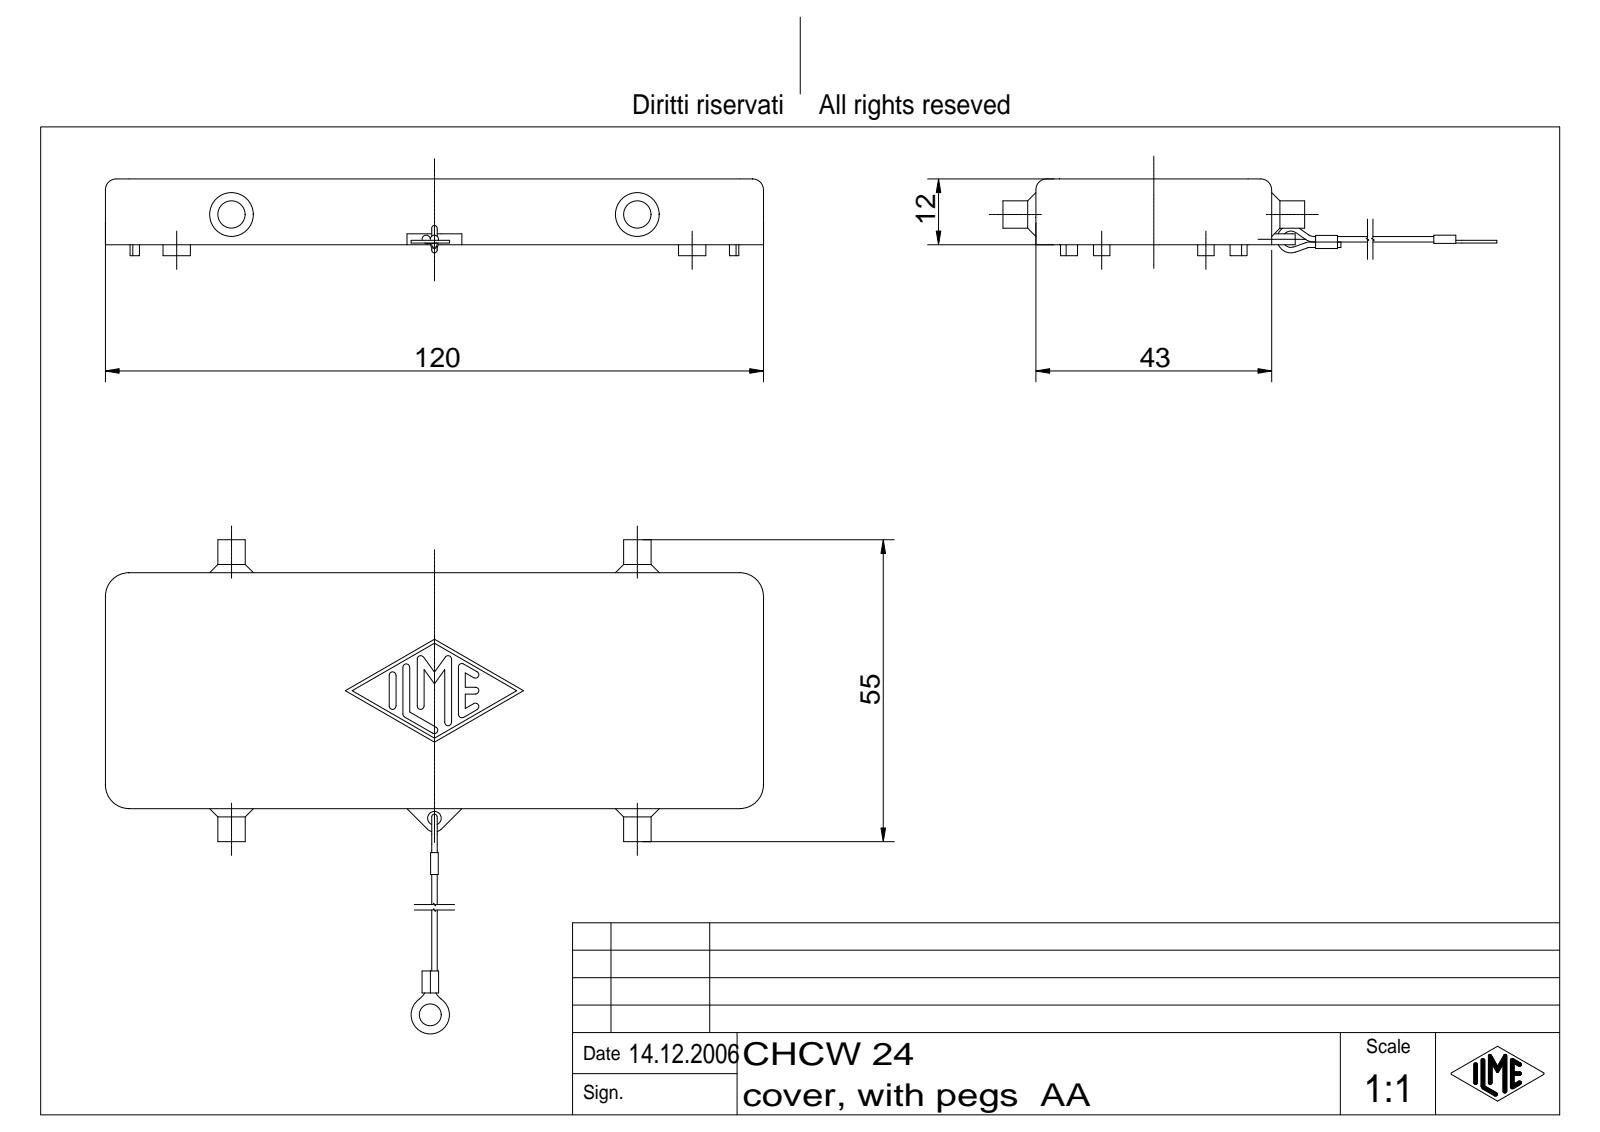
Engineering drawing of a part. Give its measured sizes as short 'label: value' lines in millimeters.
name: CHCW 24
written by: Autodesk Inventor 7 (AUTOMOTIVE_DESIGN)
unit: mm
bodies: 2 solids, 222 faces (93 planar, 73 cylindrical, 56 other)
size: 153.5 × 120 × 14
volume: 28 848 mm³; area: 17 703 mm²
holes: 1× ⌀2.5, 1× ⌀4
bosses: 4× ⌀1, 2× ⌀5, 1× ⌀7
rounds: 14× R0.62, 8× R2, 4× R0.7, 4× R4.3, 2× R0.75, 2× R1, 2× R3, 1× R1.75
face distances: 3, 4.5, 38.5, 9, 12, 43, 34, 115.5, 120, 111
hole spacings: 99.25
